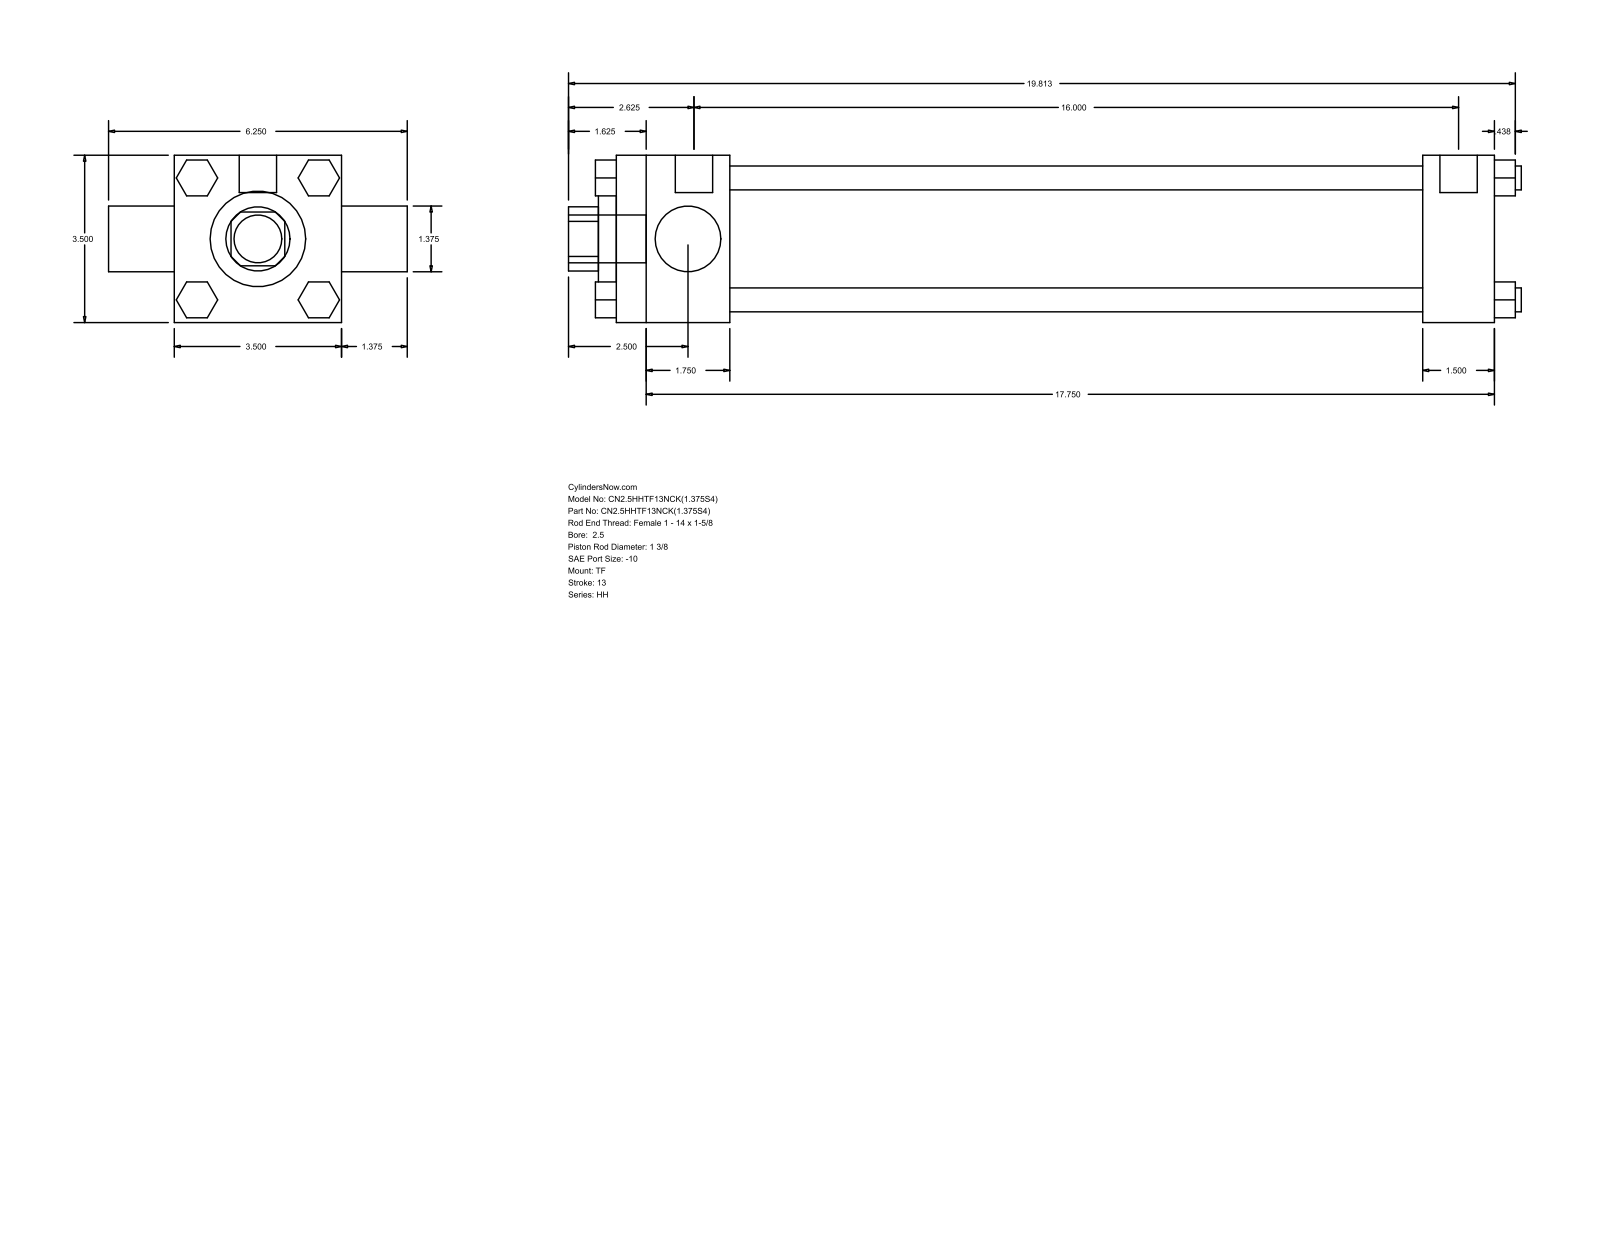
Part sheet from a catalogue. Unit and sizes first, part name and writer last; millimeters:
Units: millimetres
Overall size (bounding box): 506.41 × 158.75 × 88.9
Round holes (diameter × count): ⌀34.92 ×2, ⌀50.8 ×1, ⌀73.03 ×1
Round bosses / shafts (diameter × count): ⌀12.7 ×4, ⌀5.56 ×3, ⌀19.84 ×2, ⌀25.4 ×1
Partial cylindrical surfaces — rounded edges, fillets, slot ends (radius × count): R17.06 ×1
Main face-to-face distances: 88.9, 466.72, 60.32, 406.4, 428.62, 368.3, 38.1, 19.05, 32.38, 56.09
Bodies: 0 solids, 120 faces (92 planar, 28 cylindrical, 0 other)
Part name (STEP PRODUCT): HH_TF__0250_1.375
STEP written by: GSSL Pune (CONFIG_CONTROL_DESIGN)
